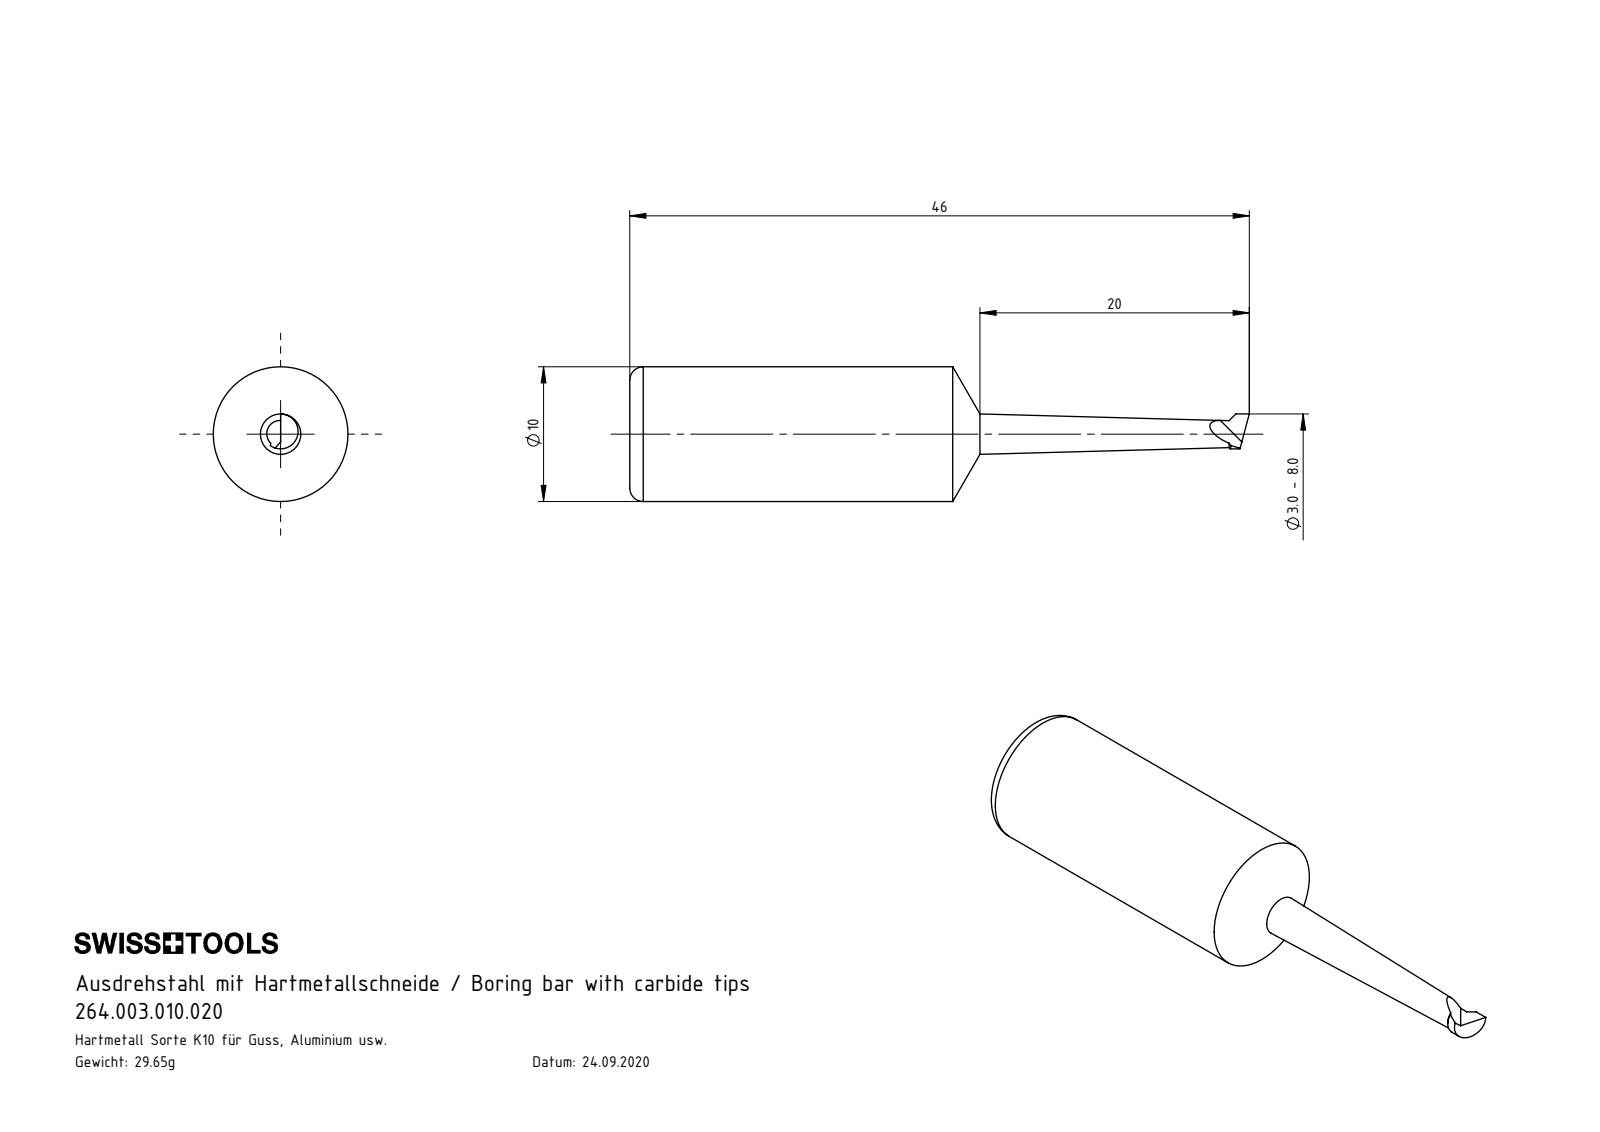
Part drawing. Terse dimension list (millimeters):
name: U10.B03.001.020
written by: SolidWorks 2017 (AUTOMOTIVE_DESIGN)
unit: mm
bodies: 1 solid, 10 faces (4 planar, 2 cylindrical, 4 other)
size: 46 × 10 × 10
volume: 2 045 mm³; area: 1 057 mm²
bosses: 1× ⌀10
rounds: 1× R1.3
